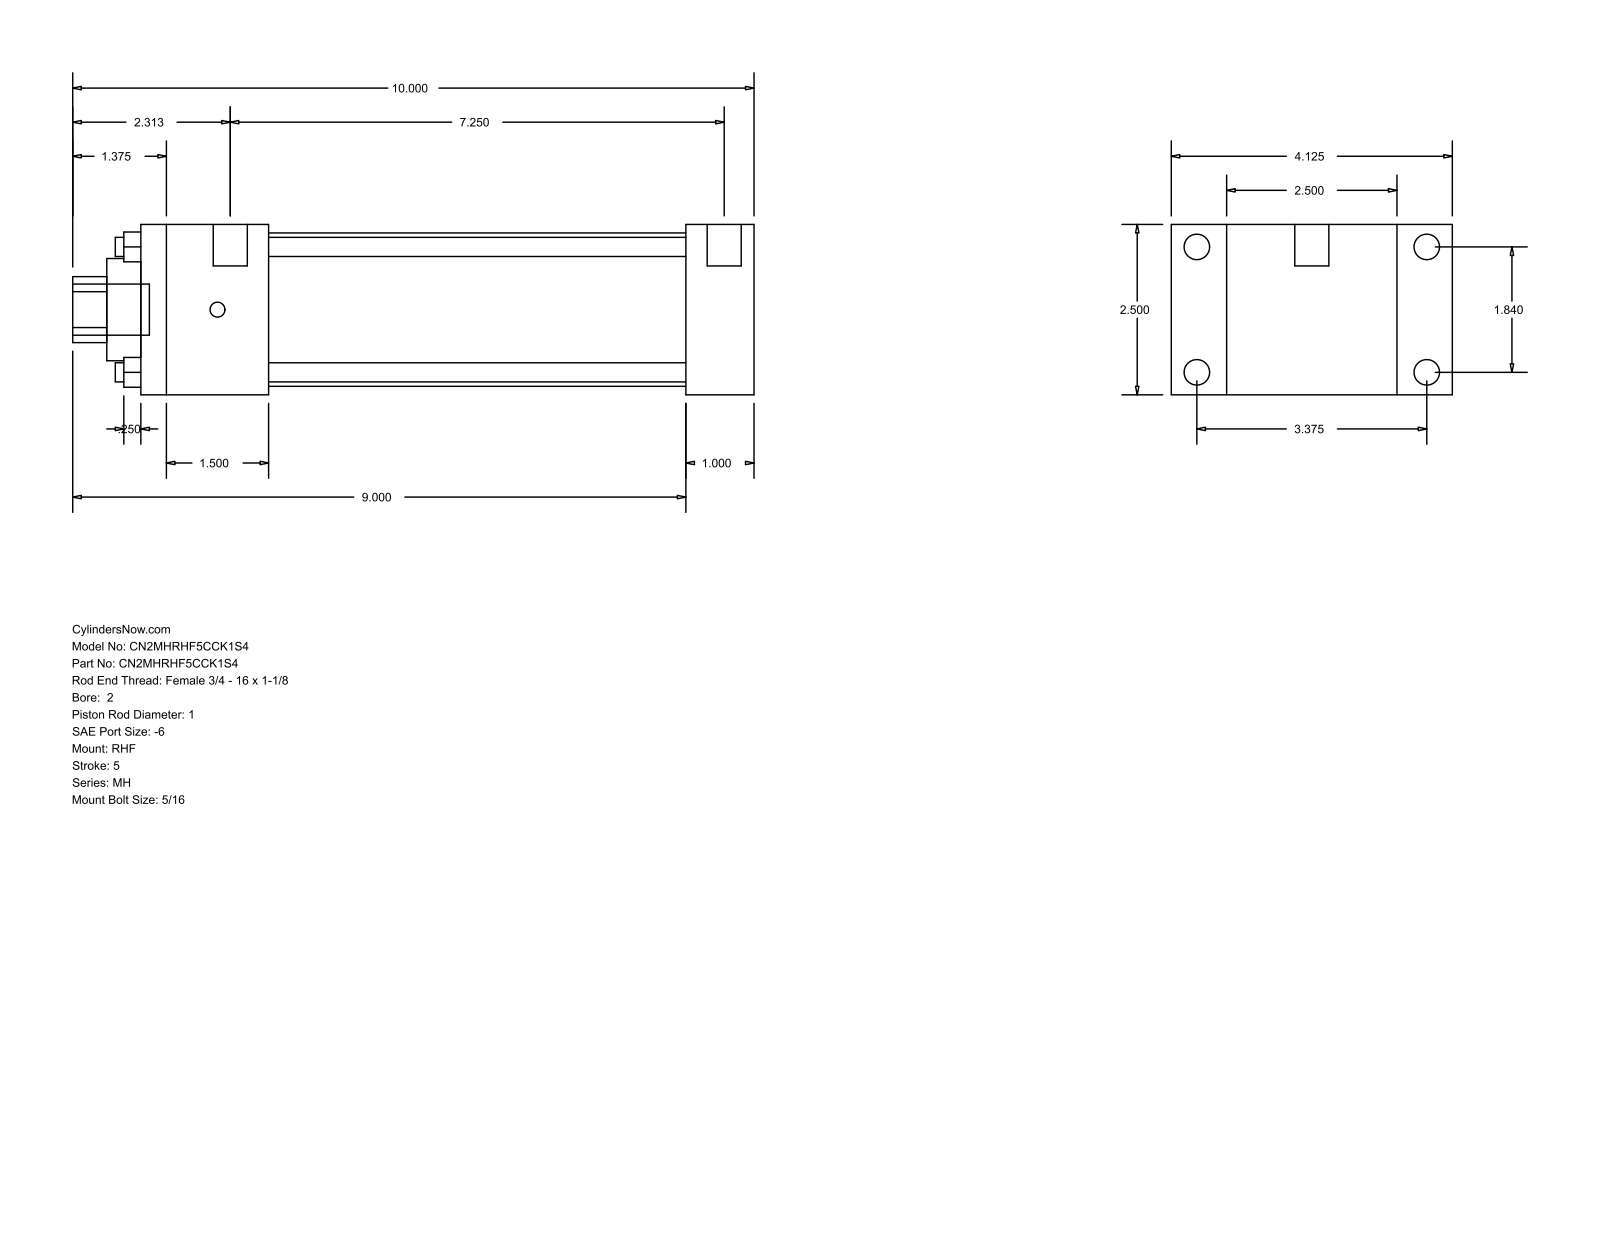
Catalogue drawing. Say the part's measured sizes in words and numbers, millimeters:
The part is named "MH_RHF__0200_1". Its 3-D file was written by "GSSL Pune (CONFIG_CONTROL_DESIGN)". It is 0 solids with 88 faces: 60 planar, 28 cylindrical and 0 other. Overall it measures 254 by 104.78 by 63.5 millimeters. Round holes: 4 of diameter 7.14, 1 of diameter 25.4, 1 of diameter 38.1, 1 of diameter 57.15. Round bosses or shafts: 4 of diameter 9.53, 4 of diameter 5.56, 2 of diameter 12.7, 1 of diameter 19.05. Partial cylindrical surfaces (rounded edges, fillets, slot ends): 1 of radius 12.29. The main face-to-face distances are 63.5, 25.4, 20.64, 84.14, 228.6, 203.2, 104.78, 47.63, 155.57, 180.97. The hole center spacings are 33.05, 46.74, 66.1.
